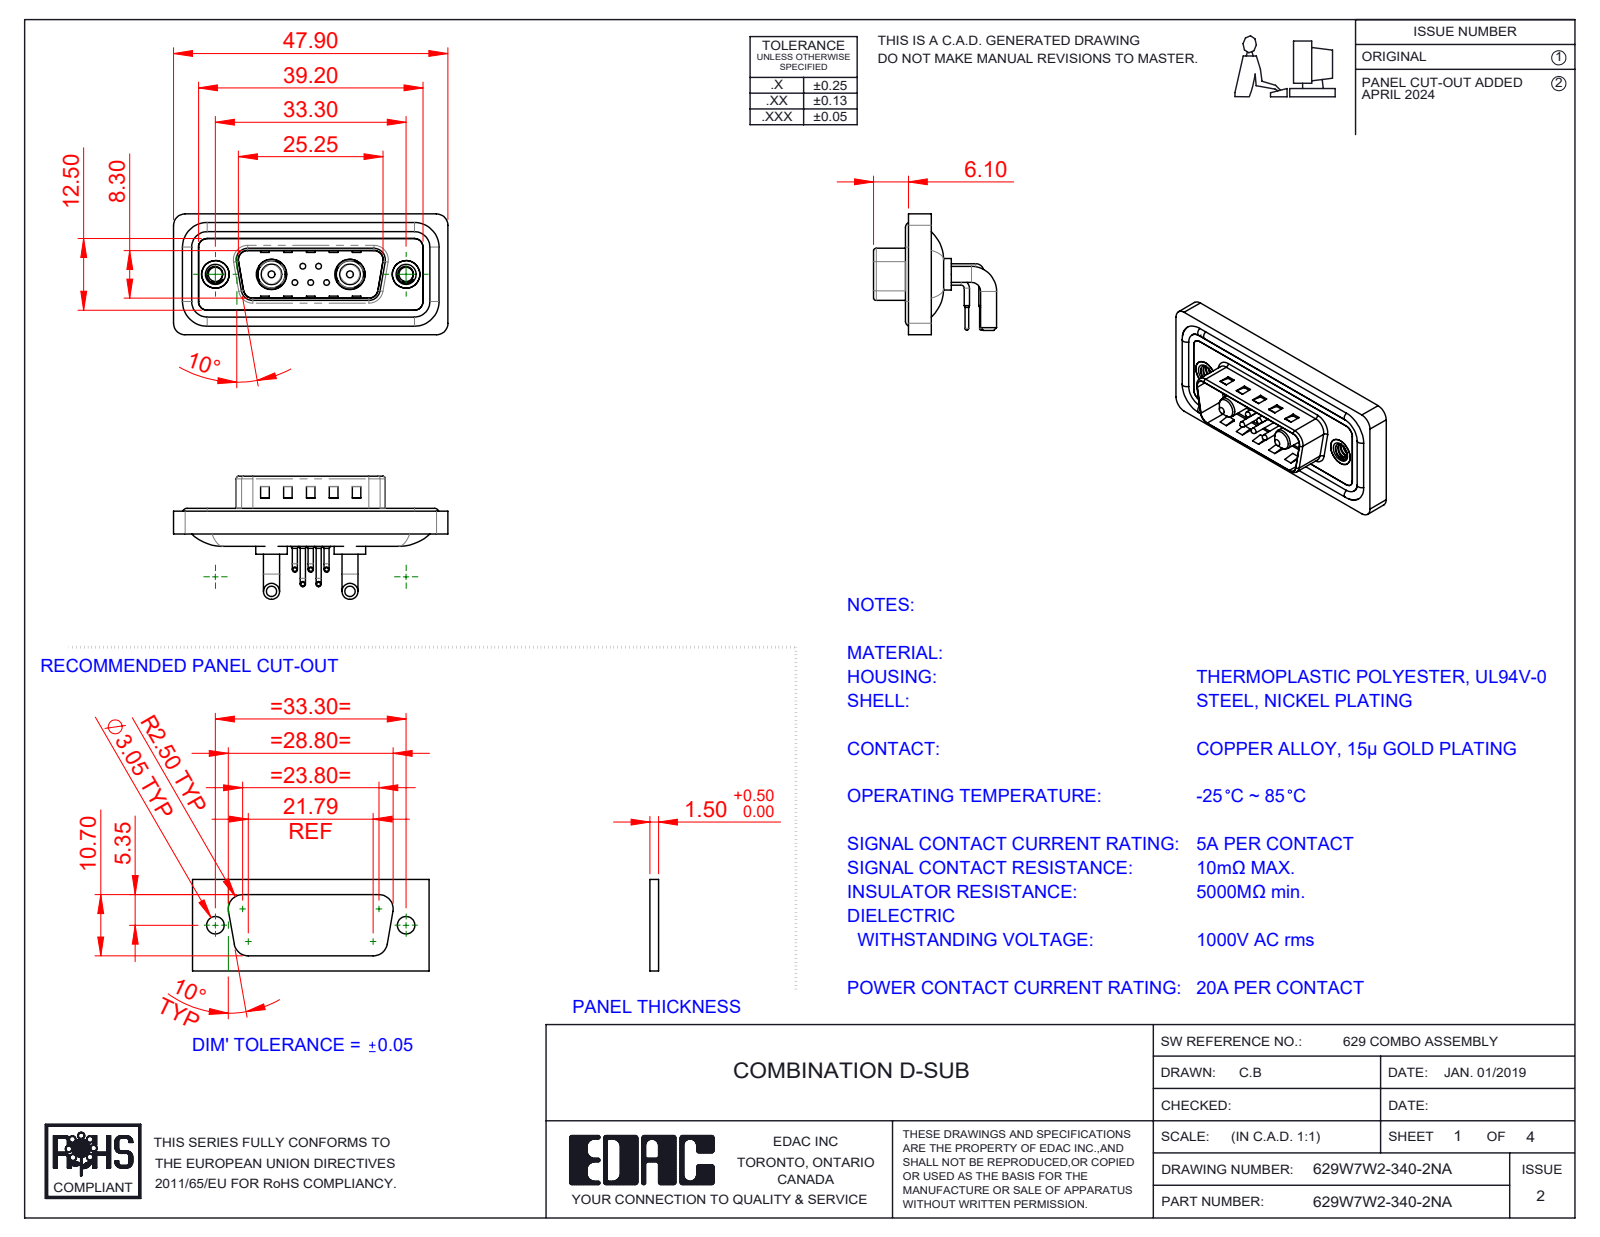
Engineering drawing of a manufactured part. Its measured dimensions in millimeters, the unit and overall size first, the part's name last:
Units: millimetres
Overall size (bounding box): 47.9 × 21.5 × 21.1
Round holes (diameter × count): ⌀0.75 ×5, ⌀1.6 ×5, ⌀2 ×5, ⌀2.5 ×2, ⌀4 ×2, ⌀4.8 ×2, ⌀4.85 ×2, ⌀5 ×2, ⌀5.3 ×2
Round bosses / shafts (diameter × count): ⌀0.9 ×10, ⌀1.5 ×5, ⌀1 ×5, ⌀0.65 ×5, ⌀2.8 ×4, ⌀1.6 ×4, ⌀5.5 ×2, ⌀5.2 ×2
Partial cylindrical surfaces — rounded edges, fillets, slot ends (radius × count): R2 ×20, R1.5 ×18, R0.5 ×8, R1.6 ×8, R1.01 ×5, R0.25 ×4, R0.6 ×4, R0.65 ×4
Main face-to-face distances: 0.4, 2.9, 0.8, 1.1, 2.1, 1.6, 2.5, 3.1, 4.5, 4.1
Hole centre spacings: 3.16, 2.77, 9.8, 23.5, 4.31, 4.33, 5.03, 5.04
Volume: 5 684 mm³ · Surface area: 9 144 mm²
Bodies: 16 solids, 1077 faces (517 planar, 404 cylindrical, 156 other)
Part name (STEP PRODUCT): 629W7W2-340-2NA; 629Combo Contact Row 2; 629Combo Contact Row 1; 629Combo Shell Rear_15 Contacts (+5 more)
STEP written by: SolidWorks 2023 (CONFIG_CONTROL_DESIGN)
